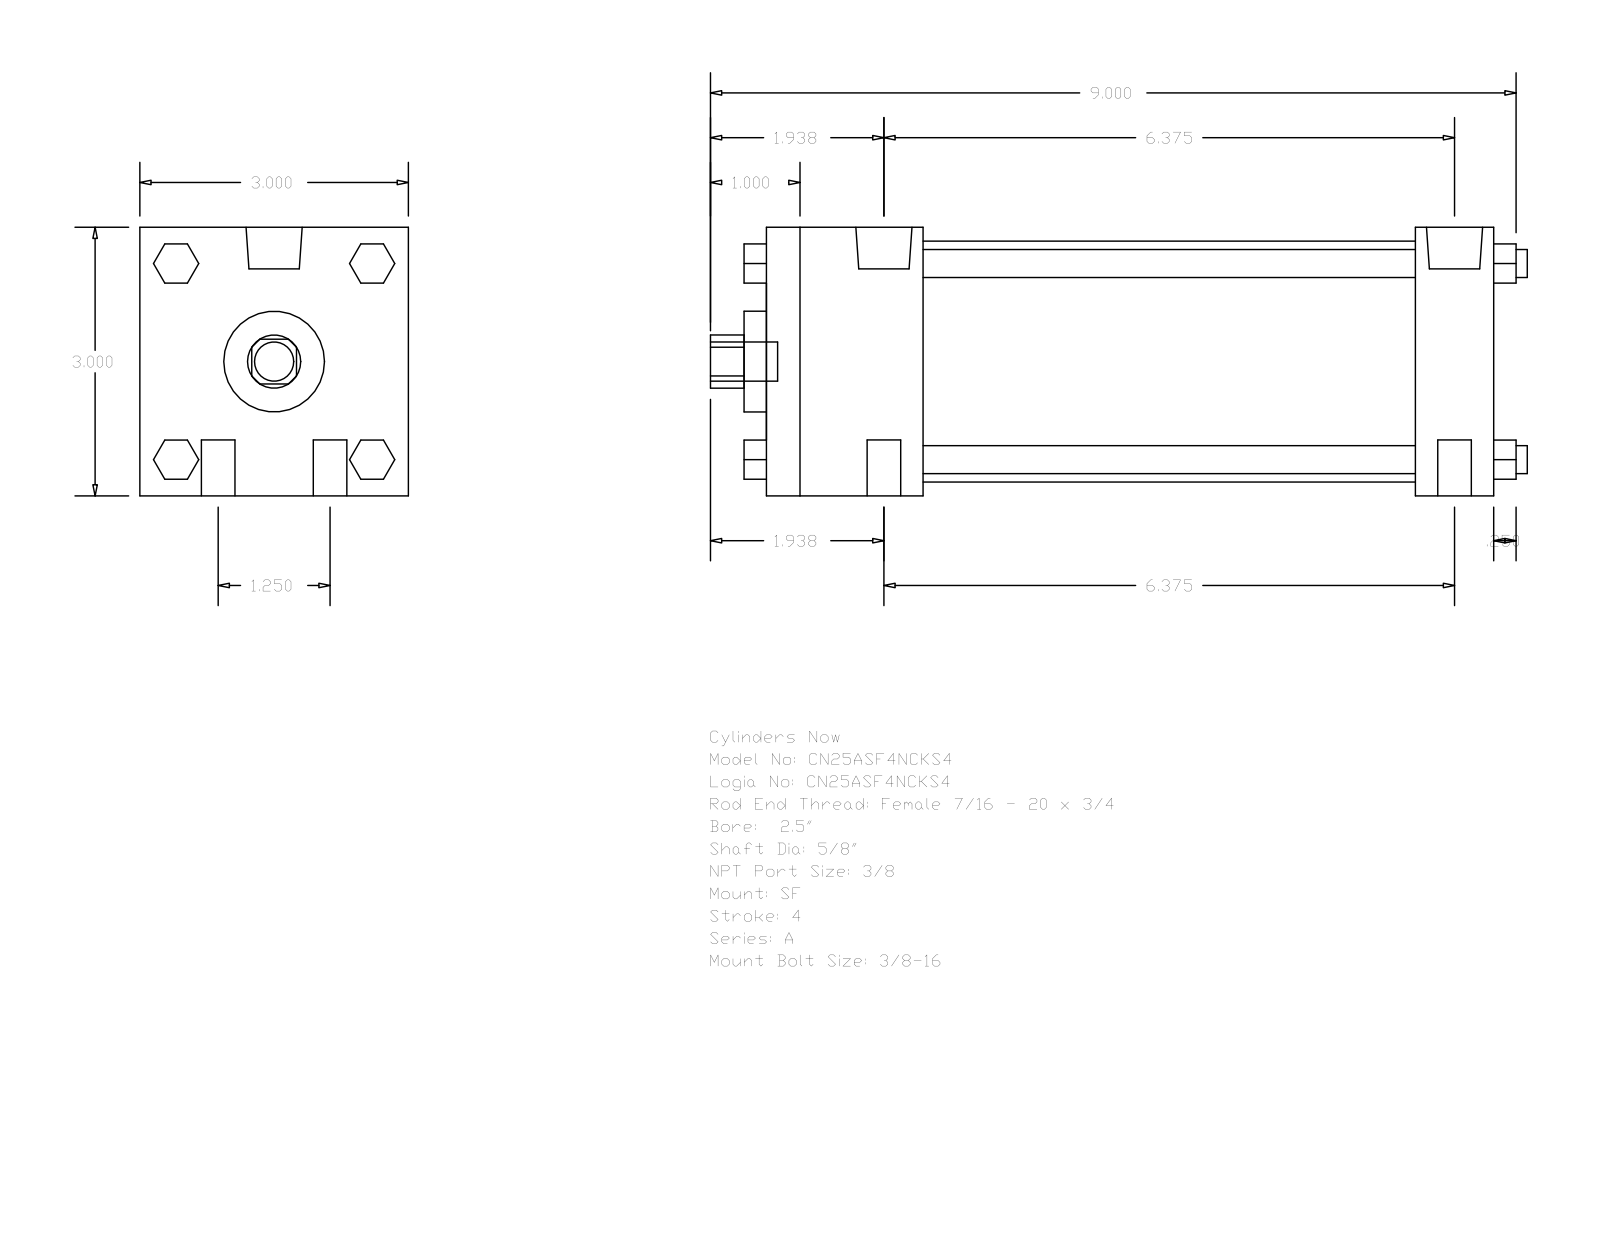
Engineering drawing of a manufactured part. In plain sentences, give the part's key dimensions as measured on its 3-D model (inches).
The part is named "A_SF__0250_0.625". Its 3-D file was written by "GSSL Pune (CONFIG_CONTROL_DESIGN)". It is 0 solids with 124 faces: 94 planar, 30 cylindrical and 0 other. Overall it measures 9.125 by 3 by 3 inches. Round holes: 1 of diameter 0.625, 1 of diameter 1.125, 1 of diameter 2.69. Round bosses or shafts: 4 of diameter 0.375, 4 of diameter 0.313, 2 of diameter 0.627, 2 of diameter 0.219, 1 of diameter 0.437. Partial cylindrical surfaces (rounded edges, fillets, slot ends): 1 of radius 0.297. The main face-to-face distances are 3, 8.125, 1.75, 7.25, 0.875, 5.5, 6.375, 0.25, 8.375, 2.
